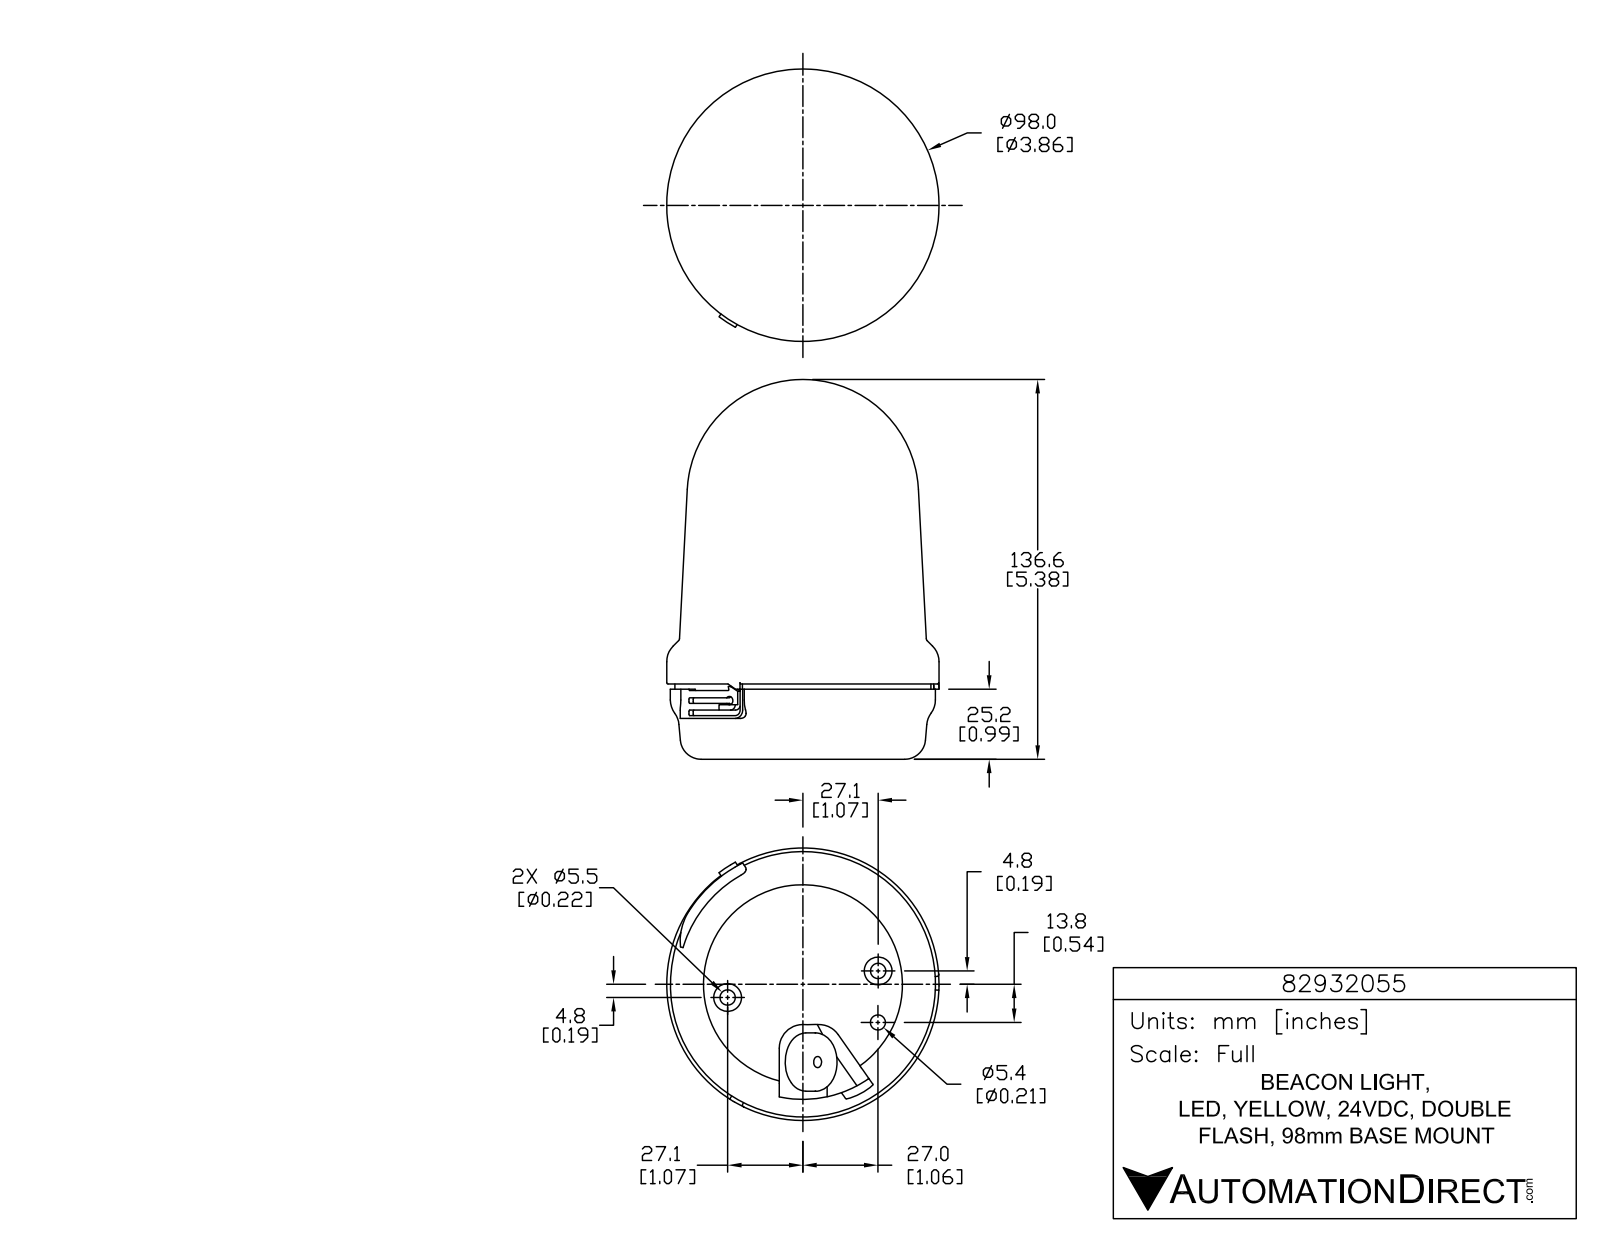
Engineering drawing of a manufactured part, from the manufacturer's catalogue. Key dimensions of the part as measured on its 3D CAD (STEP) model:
Part name (STEP PRODUCT): 82932055
STEP written by: SolidWorks 2015 (AUTOMOTIVE_DESIGN)
Units: inches
Bodies: 1 solid, 872 faces (566 planar, 204 cylindrical, 102 other)
Overall size (bounding box): 5.378 × 3.858 × 3.858
Volume: 44.69 in³ · Surface area: 73.66 in²
Round holes (diameter × count): ⌀0.059 ×3, ⌀0.217 ×2, ⌀0.157 ×1, ⌀0.213 ×1, ⌀2.819 ×1
Round bosses / shafts (diameter × count): ⌀0.339 ×3, ⌀0.084 ×3, ⌀0.394 ×2, ⌀3.858 ×1, ⌀3.756 ×1, ⌀3.626 ×1, ⌀0.827 ×1
Partial cylindrical surfaces — rounded edges, fillets, slot ends (radius × count): R0.005 ×9, R0.005 ×6, R0.012 ×6, R0.012 ×6, R0.012 ×6, R0.196 ×6, R0.02 ×5, R0.039 ×4
Main face-to-face distances: 1.045, 0.972, 0.073, 0.02, 0.992, 1.065, 0.236, 0.579, 0.559, 0.413
Hole centre spacings: 1.083, 0.73, 1.193, 2.158, 2.165
